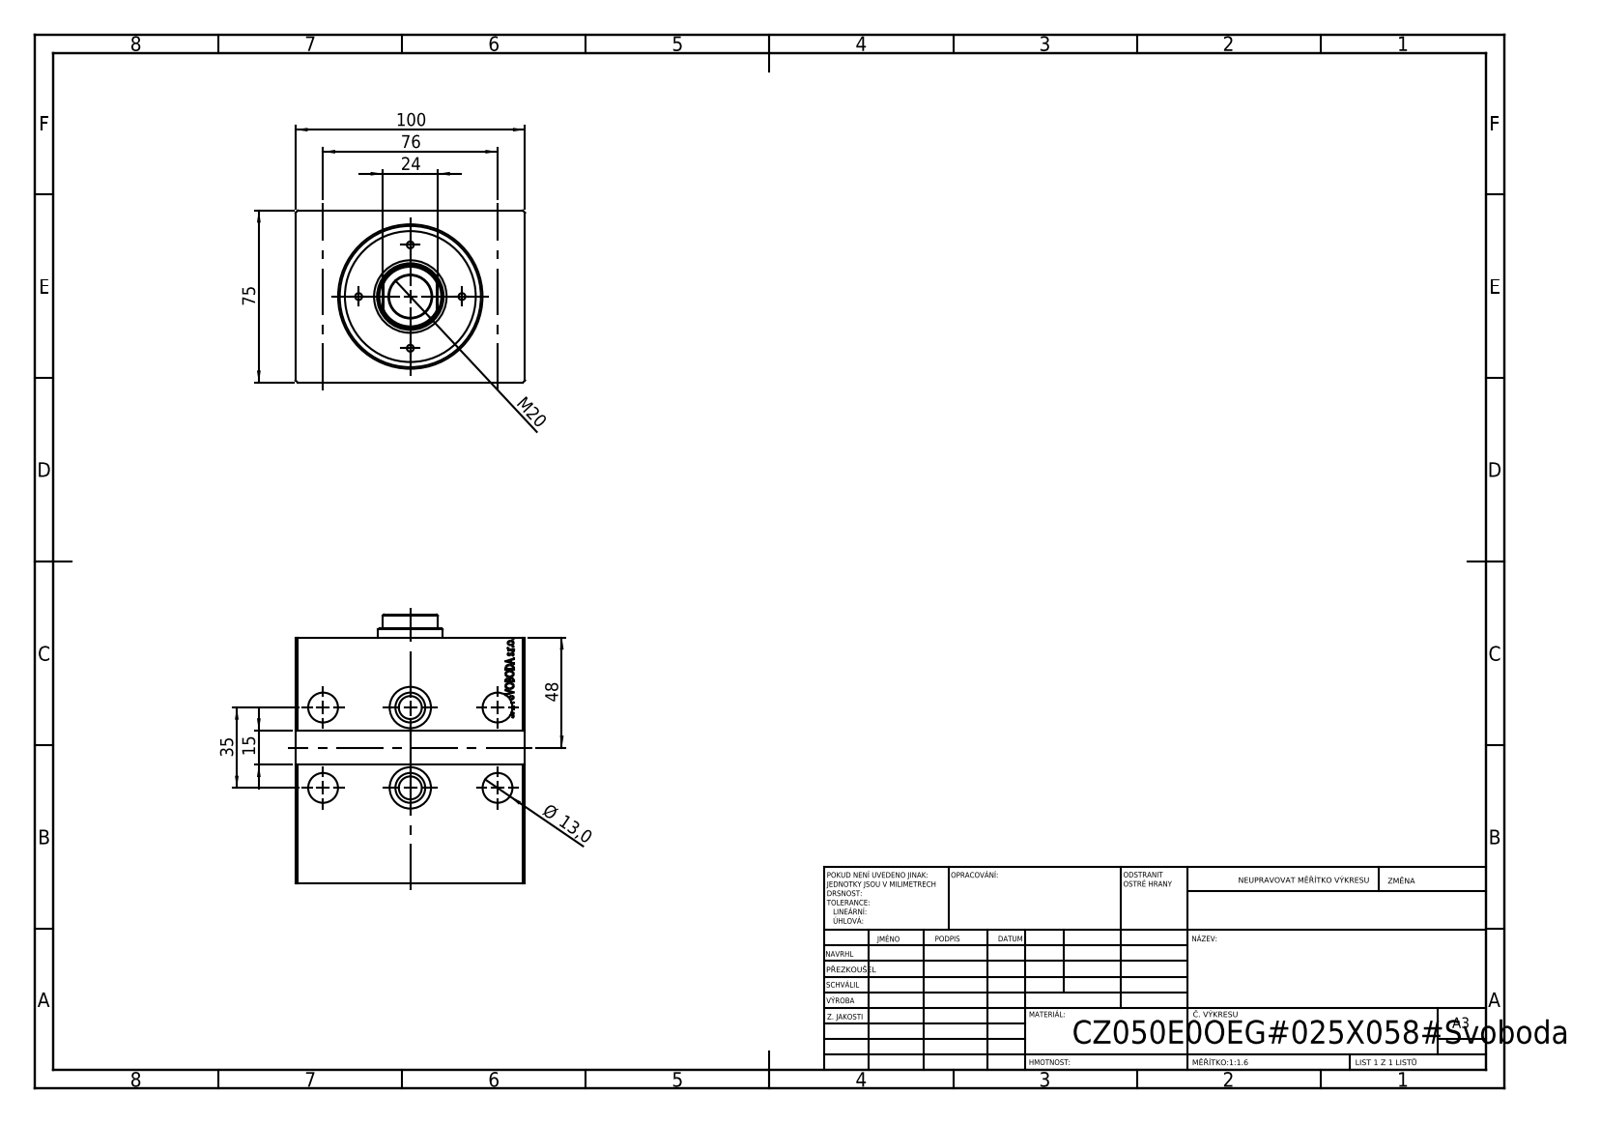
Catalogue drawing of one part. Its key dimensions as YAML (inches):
step_written_by: "SolidWorks 2019 (CONFIG_CONTROL_DESIGN)"
units: inches
bodies: {solids: 1, faces: 775, planar: 375, cylindrical: 30, other: 370}
overall_size: [4.213, 3.937, 2.953]
volume: 34.96
surface_area: 122.1
round_holes:
  - {diameter: 0.512, count: 4}
  - {diameter: 0.315, count: 2}
  - {diameter: 0.394, count: 2}
  - {diameter: 0.709, count: 2}
  - {diameter: 1.417, count: 1}
  - {diameter: 1.969, count: 1}
  - {diameter: 2.421, count: 1}
round_bosses_or_shafts:
  - {diameter: 0.512, count: 2}
face_to_face_distances: [2.953, 3.937, 4.213, 3.512, 0.701, 0.079, 2.874, 4.205, 0.693, 0.394]
hole_center_spacings: [1.496, 2.034, 1.378, 2.992, 3.294, 0.754, 0.828, 0.863]
